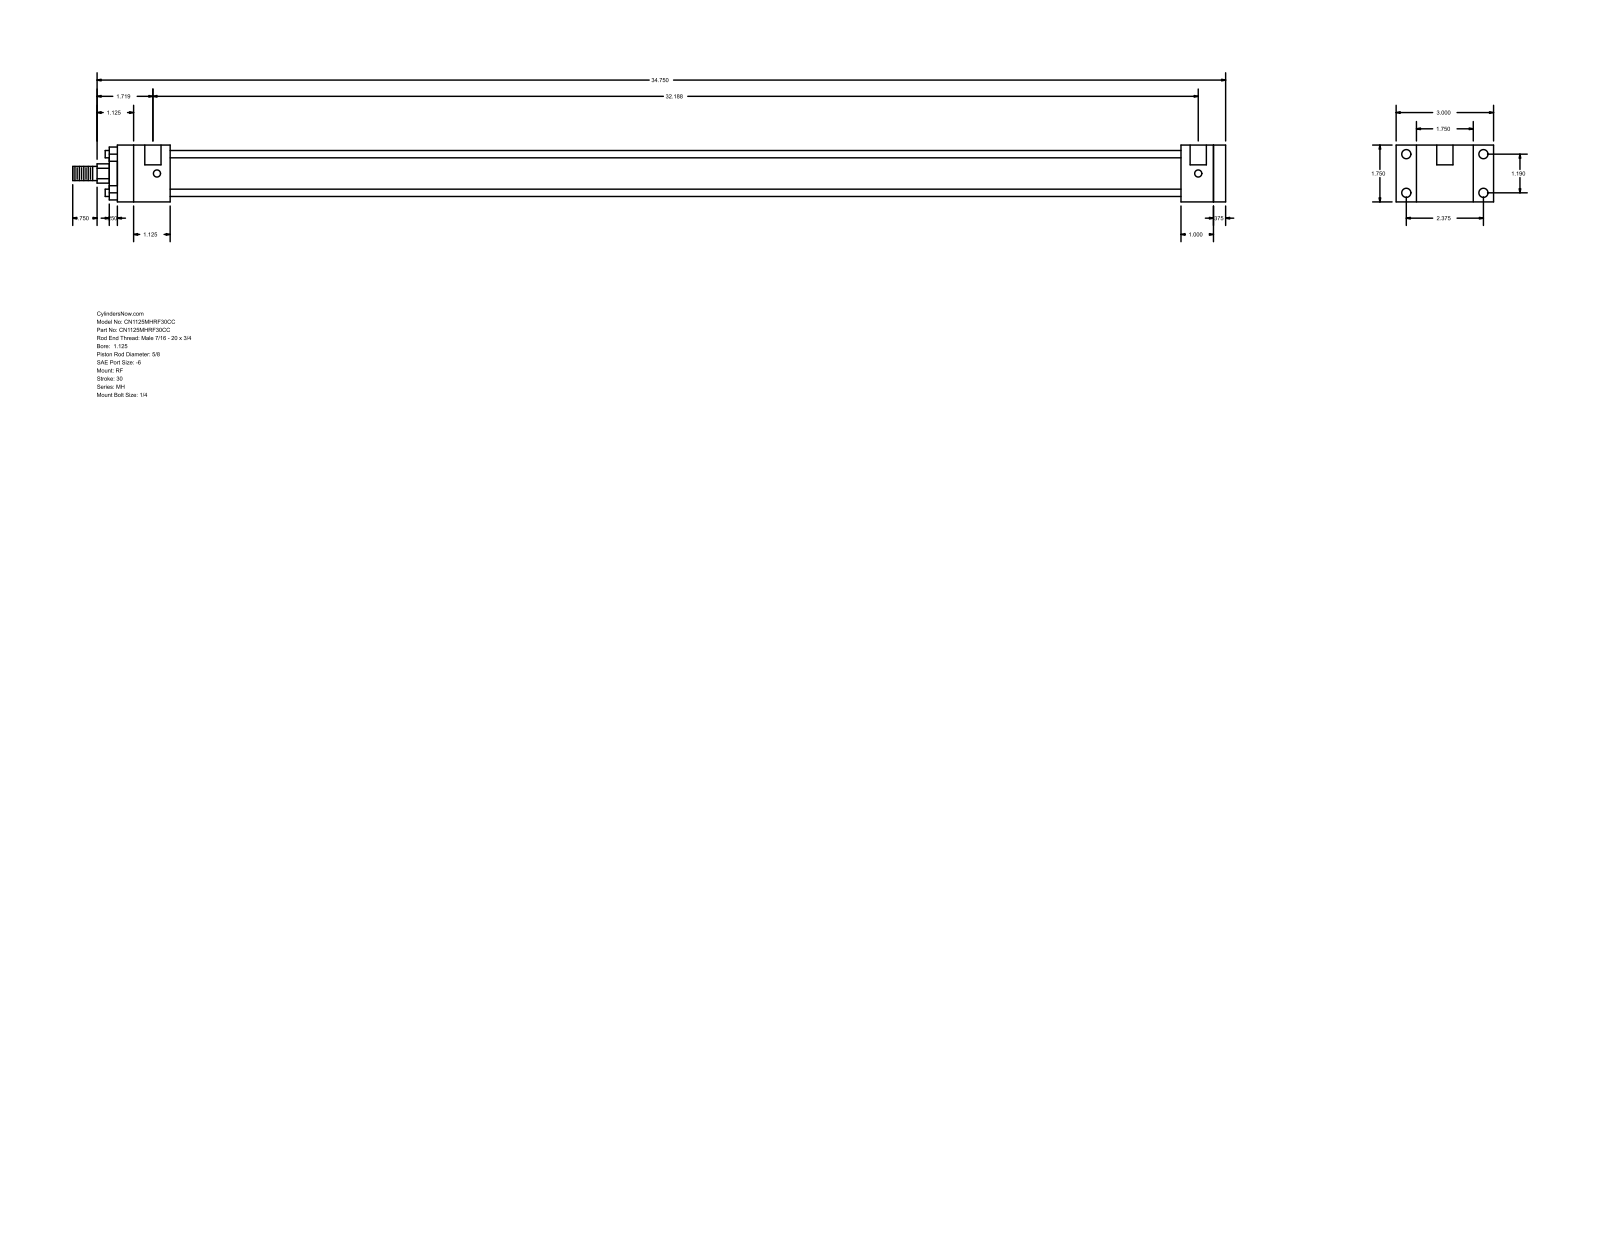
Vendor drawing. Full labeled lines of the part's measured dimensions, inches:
Part name (STEP PRODUCT): MH_RF__0112_0.625
STEP written by: GSSL Pune (CONFIG_CONTROL_DESIGN)
Units: inches
Bodies: 0 solids, 92 faces (64 planar, 28 cylindrical, 0 other)
Overall size (bounding box): 35.5 × 3 × 1.75
Round holes (diameter × count): ⌀0.219 ×4, ⌀0.281 ×4, ⌀0.5 ×2
Round bosses / shafts (diameter × count): ⌀0.225 ×4, ⌀1.375 ×1, ⌀1.125 ×1, ⌀0.625 ×1, ⌀0.437 ×1
Partial cylindrical surfaces — rounded edges, fillets, slot ends (radius × count): R0.297 ×1
Main face-to-face distances: 1.75, 0.375, 34.125, 0.625, 32.125, 32.5, 31.125, 1, 1.375, 1.625
Hole centre spacings: 1.19, 2.375, 2.656, 32.063, 0.125, 32.187
